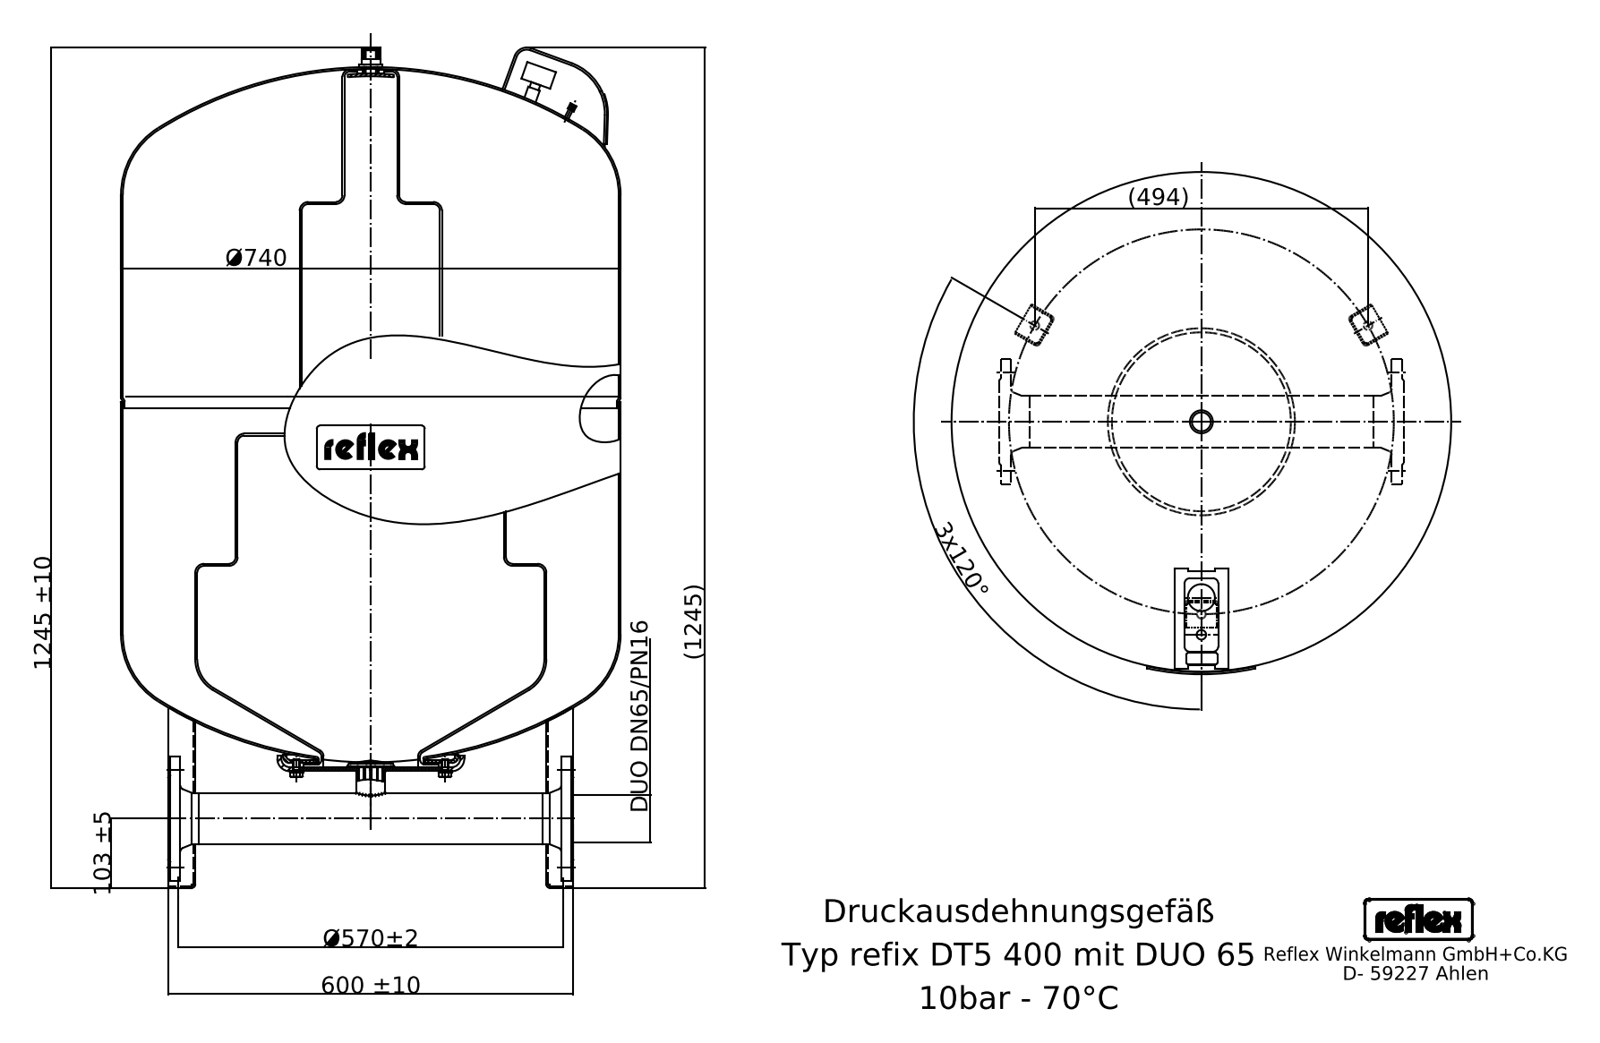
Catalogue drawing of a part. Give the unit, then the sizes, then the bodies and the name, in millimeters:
Units: millimetres
Overall size (bounding box): 1245 × 740 × 740
Round holes (diameter × count): ⌀19 ×4, ⌀13.4 ×3, ⌀2.48 ×1, ⌀7 ×1, ⌀8 ×1, ⌀11.4 ×1, ⌀76.1 ×1, ⌀157 ×1, ⌀250 ×1
Round bosses / shafts (diameter × count): ⌀10 ×9, ⌀740 ×1, ⌀260 ×1, ⌀230 ×1, ⌀185 ×1, ⌀62 ×1, ⌀42.4 ×1, ⌀34 ×1
Partial cylindrical surfaces — rounded edges, fillets, slot ends (radius × count): R1 ×15, R2.5 ×15, R5 ×15, R5.62 ×4, R2.25 ×3, R3.84 ×2, R6.75 ×2, R8 ×2
Main face-to-face distances: 652, 2.5, 47.5, 196, 848, 6, 202, 854, 5, 50
Hole centre spacings: 72.51, 102.54, 285, 493.64, 145.01
Volume: 391 600 000 mm³ · Surface area: 5 206 000 mm²
Bodies: 23 solids, 513 faces (225 planar, 180 cylindrical, 108 other)
STEP written by: Mechanical Desktop 2008 (CONFIG_CONTROL_DESIGN)
